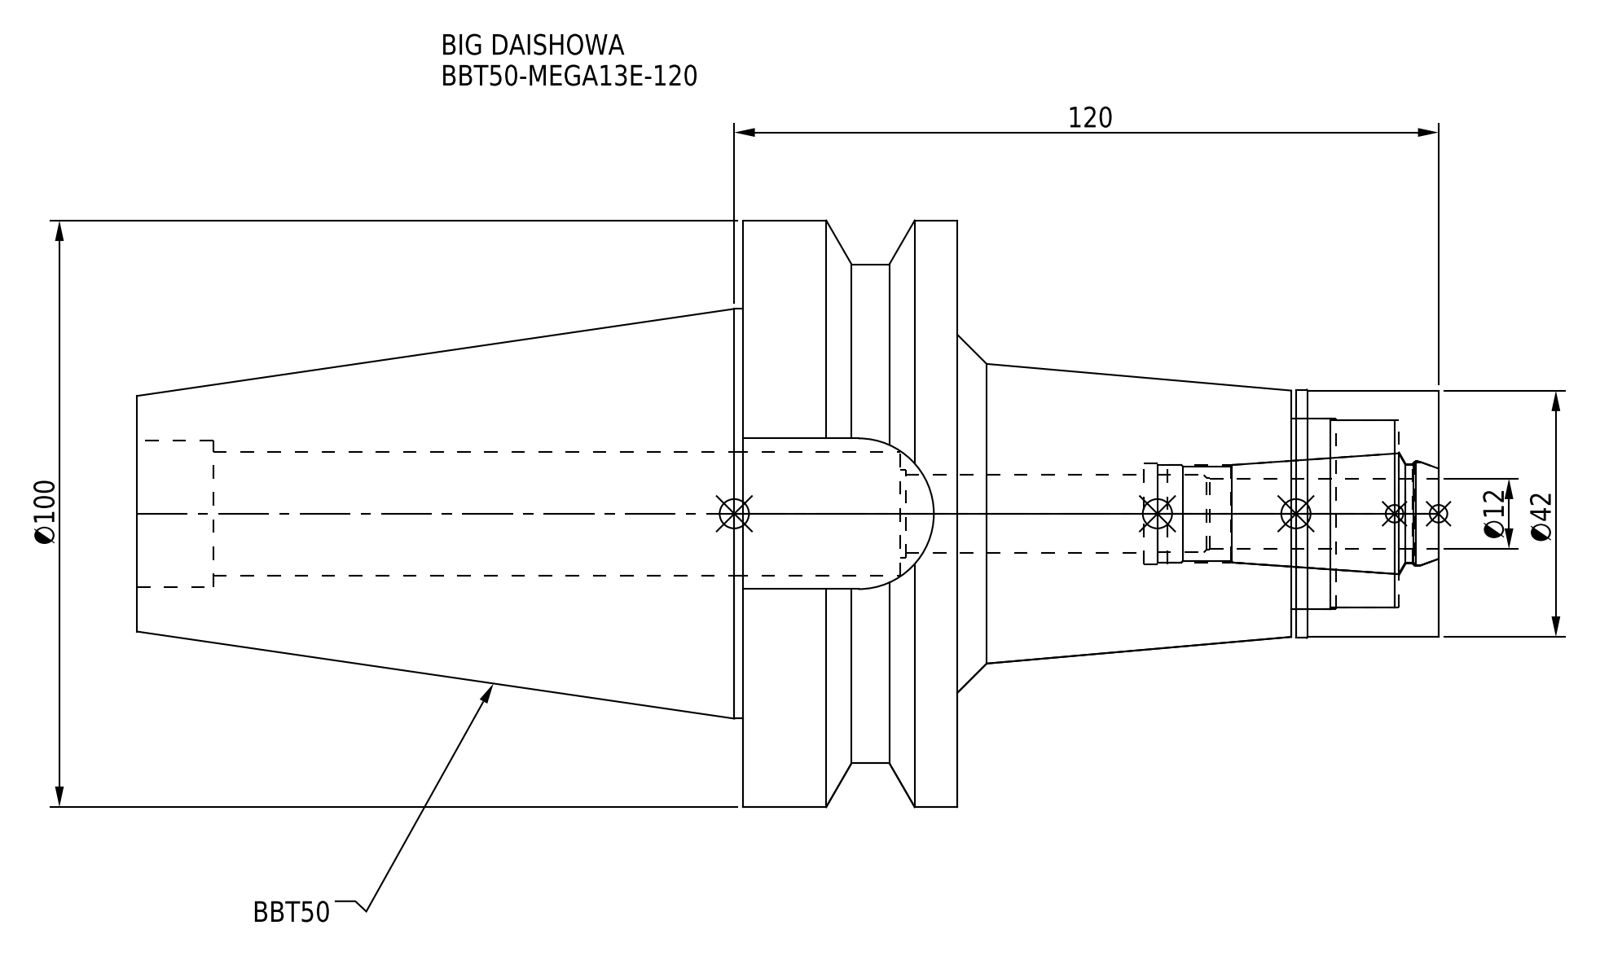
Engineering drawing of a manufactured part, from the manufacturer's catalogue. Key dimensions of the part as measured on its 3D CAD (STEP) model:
Part name (STEP PRODUCT): BBT50-MEGA13E-120_1.stp; BBT50ME13120-120_ASM.stp; BBT50-MEGA13E-120-120-FreeParts; MEN13_1.stp (+3 more)
STEP written by: SolidWorks 2019 (CONFIG_CONTROL_DESIGN)
Units: millimetres
Bodies: 2 solids, 81 faces (21 planar, 40 cylindrical, 20 other)
Overall size (bounding box): 221.8 × 100 × 100
Volume: 567 781 mm³ · Surface area: 74 762 mm²
Round holes (diameter × count): ⌀13.3 ×1, ⌀15 ×1, ⌀16.6 ×1, ⌀17 ×1, ⌀17.2 ×1, ⌀17.9 ×1, ⌀21.2 ×1, ⌀25 ×1, ⌀32 ×1, ⌀32.5 ×1
Round bosses / shafts (diameter × count): ⌀100 ×1, ⌀85 ×1, ⌀69.85 ×1, ⌀42.3 ×1, ⌀42 ×1
Partial cylindrical surfaces — rounded edges, fillets, slot ends (radius × count): R12.85 ×1
Main face-to-face distances: 36.5, 82, 118.5, 221.8, 139.8, 103.3, 70.8, 25.1, 24.3, 57.7
